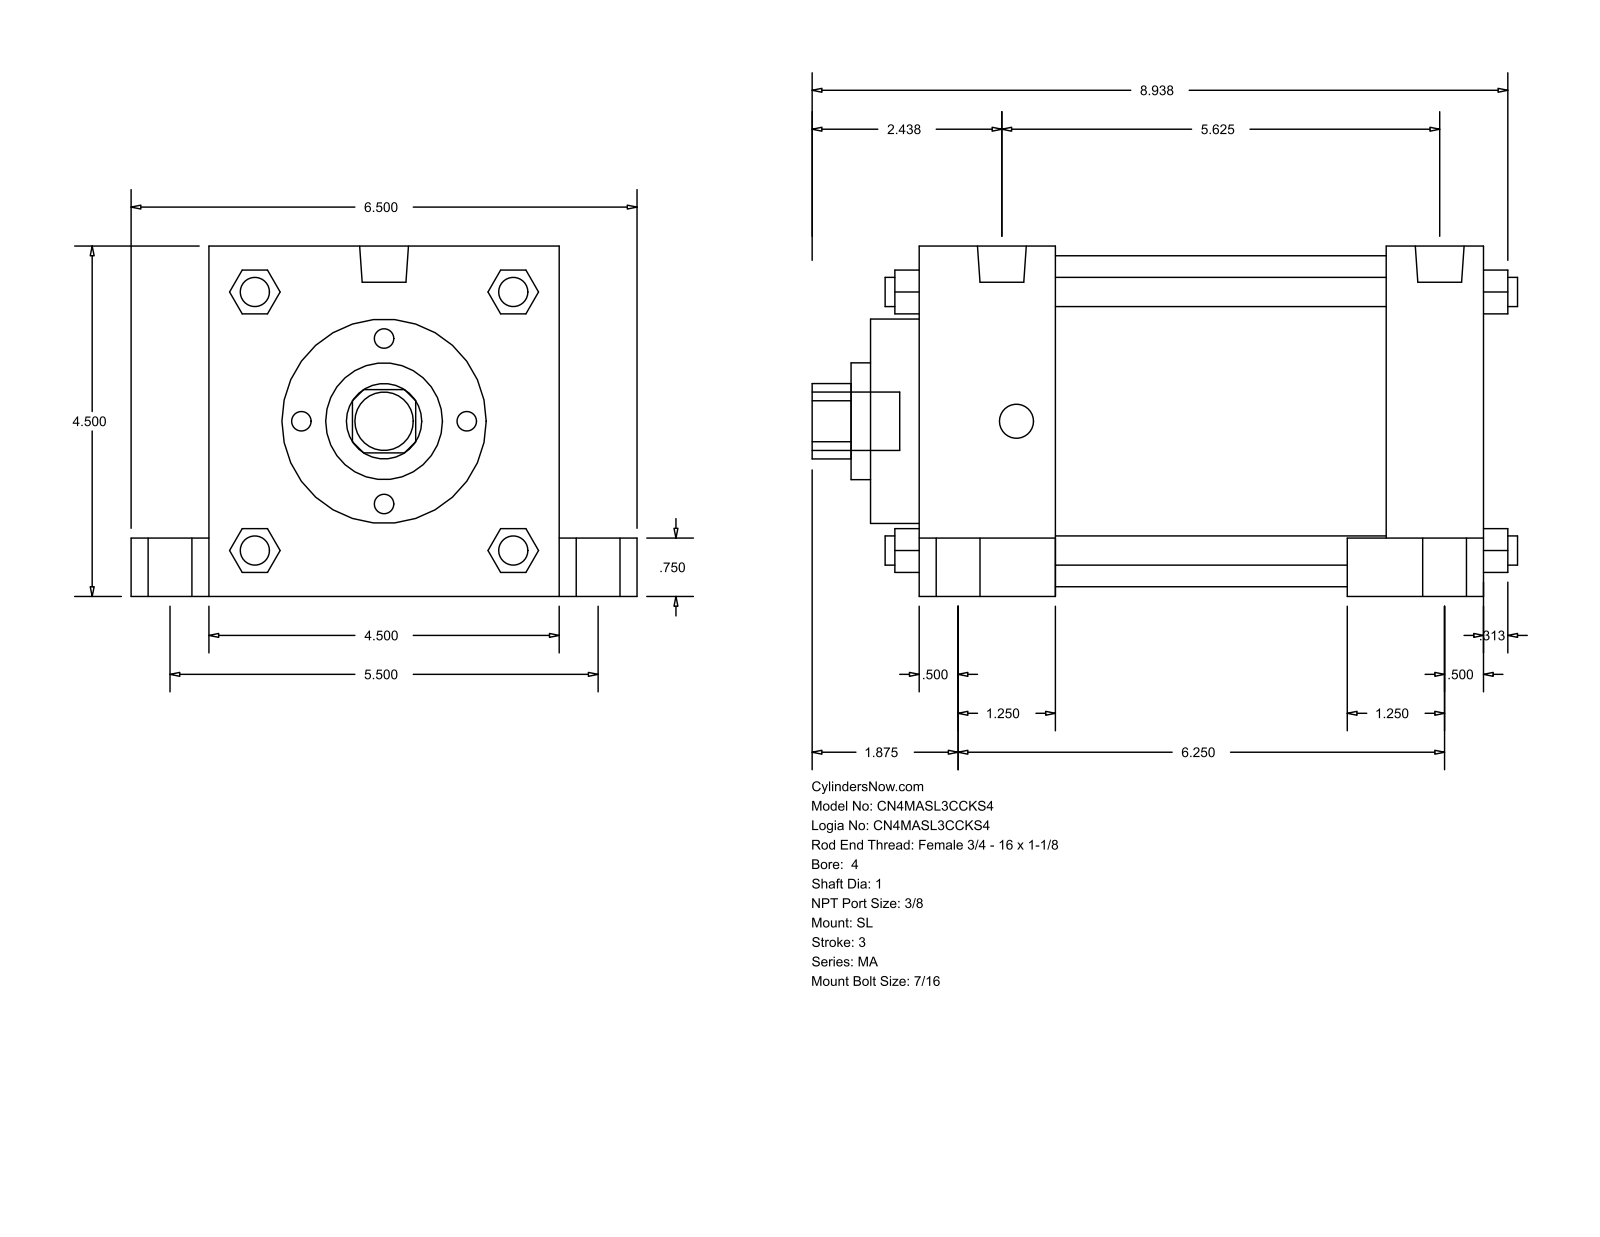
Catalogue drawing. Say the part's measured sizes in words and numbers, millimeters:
The part is named "MA_SL__0400_1". Its 3-D file was written by "GSSL Pune (CONFIG_CONTROL_DESIGN)". It is 0 solids with 150 faces: 113 planar, 37 cylindrical and 0 other. Overall it measures 230.19 by 165.1 by 114.3 millimeters. Round holes: 1 of diameter 25.4, 1 of diameter 38.1, 1 of diameter 66.67, 1 of diameter 107.95. Round bosses or shafts: 4 of diameter 20.64, 4 of diameter 14.29, 4 of diameter 11.11, 4 of diameter 9.53, 2 of diameter 15.93, 1 of diameter 19.05. Partial cylindrical surfaces (rounded edges, fillets, slot ends): 1 of radius 12.29. The main face-to-face distances are 114.3, 184.15, 44.46, 139.69, 152.4, 107.94, 31.75, 25.4, 139.7, 200.02.
